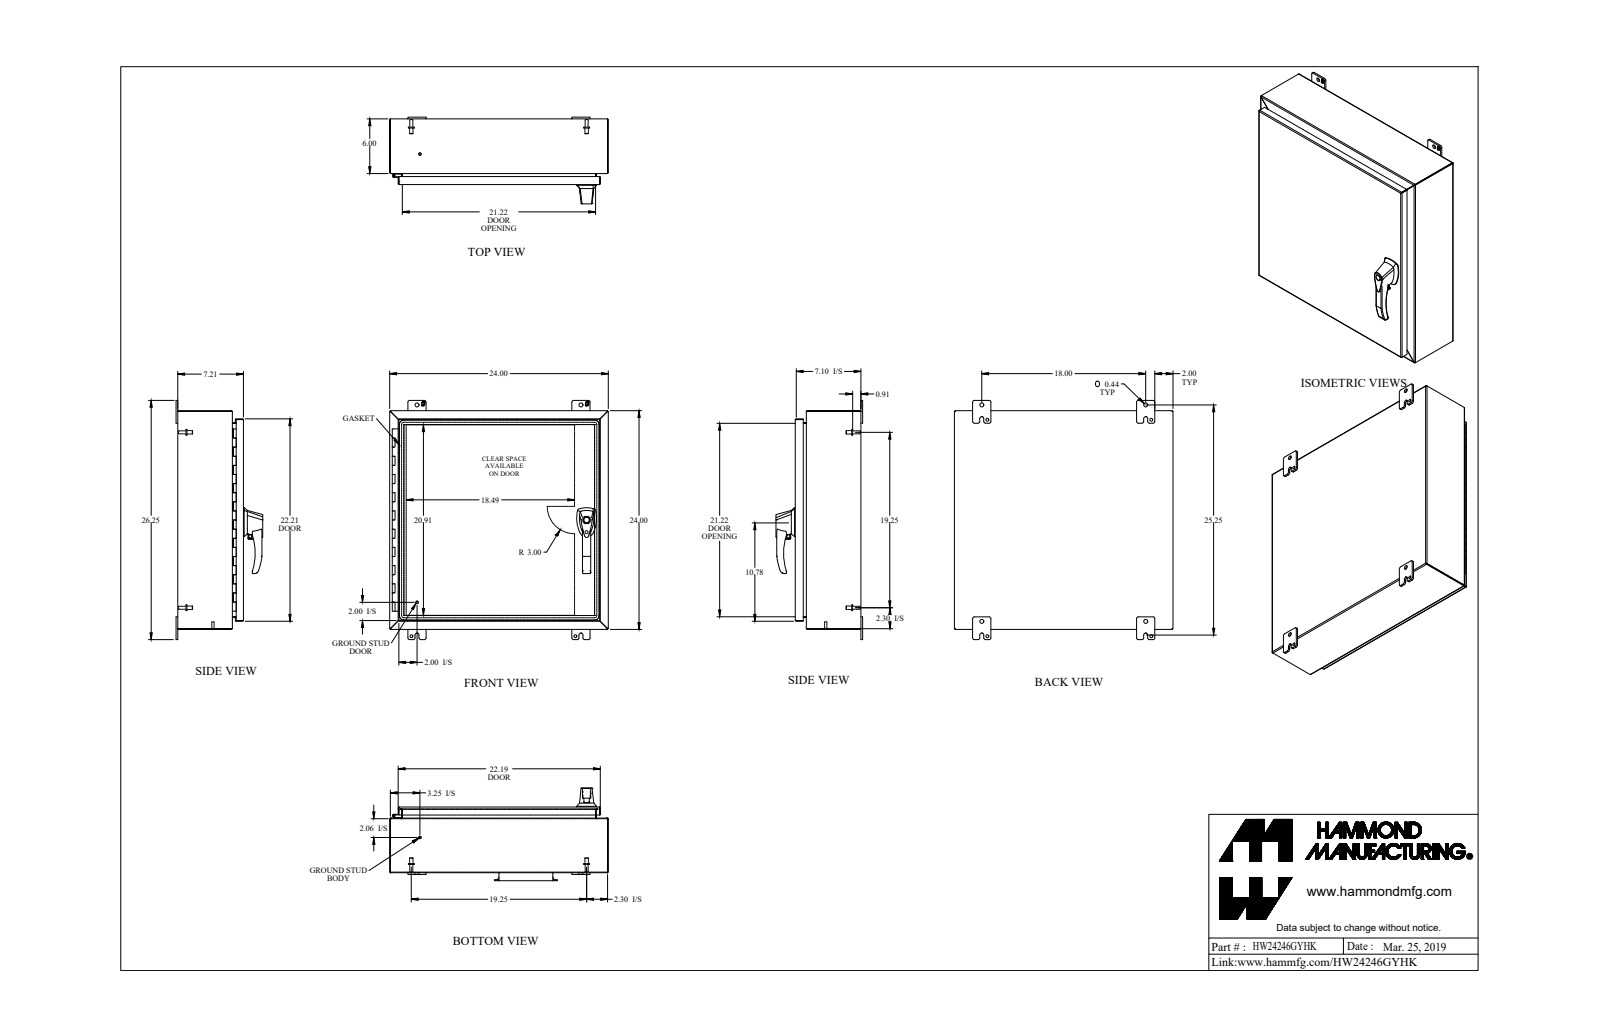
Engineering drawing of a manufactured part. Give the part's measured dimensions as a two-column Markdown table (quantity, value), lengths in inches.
| quantity | value |
| --- | --- |
| part name | HW24246GYHK |
| STEP written by | SolidWorks 2018 (AUTOMOTIVE_DESIGN) |
| units | inches |
| bodies | 46 solids, 1508 faces (766 planar, 560 cylindrical, 182 other) |
| overall size | 26.25 × 24 × 9.512 |
| volume | 174.5 in³ |
| surface area | 4 443 in² |
| round holes (diameter × count) | 0.176 × 6, 0.25 × 4, 0.313 × 4, 0.196 × 3, 0.265 × 3, 0.413 × 3, 0.256 × 2, 0.394 × 2, 0.437 × 2, 0.187 × 1, 0.233 × 1, 0.334 × 1 |
| round bosses / shafts (diameter × count) | 0.375 × 9, 0.25 × 6, 0.156 × 6, 0.65 × 4, 0.33 × 4, 1 × 3, 0.63 × 2, 0.51 × 2 |
| partial cylindrical surfaces (radius × count) | 0.25 × 27, 0.188 × 24, 0.036 × 20, 0.108 × 20, 0.06 × 12, 0.125 × 9, 0.045 × 8, 0.218 × 8 |
| main face-to-face distances | 0.072, 0.072, 23.928, 7.138, 7.066, 7.21, 7.138, 23.856, 24, 5.928 |
| hole center spacings | 8.118, 8.119, 16.237, 1.111, 8.067, 8.119, 18, 1.005 |
